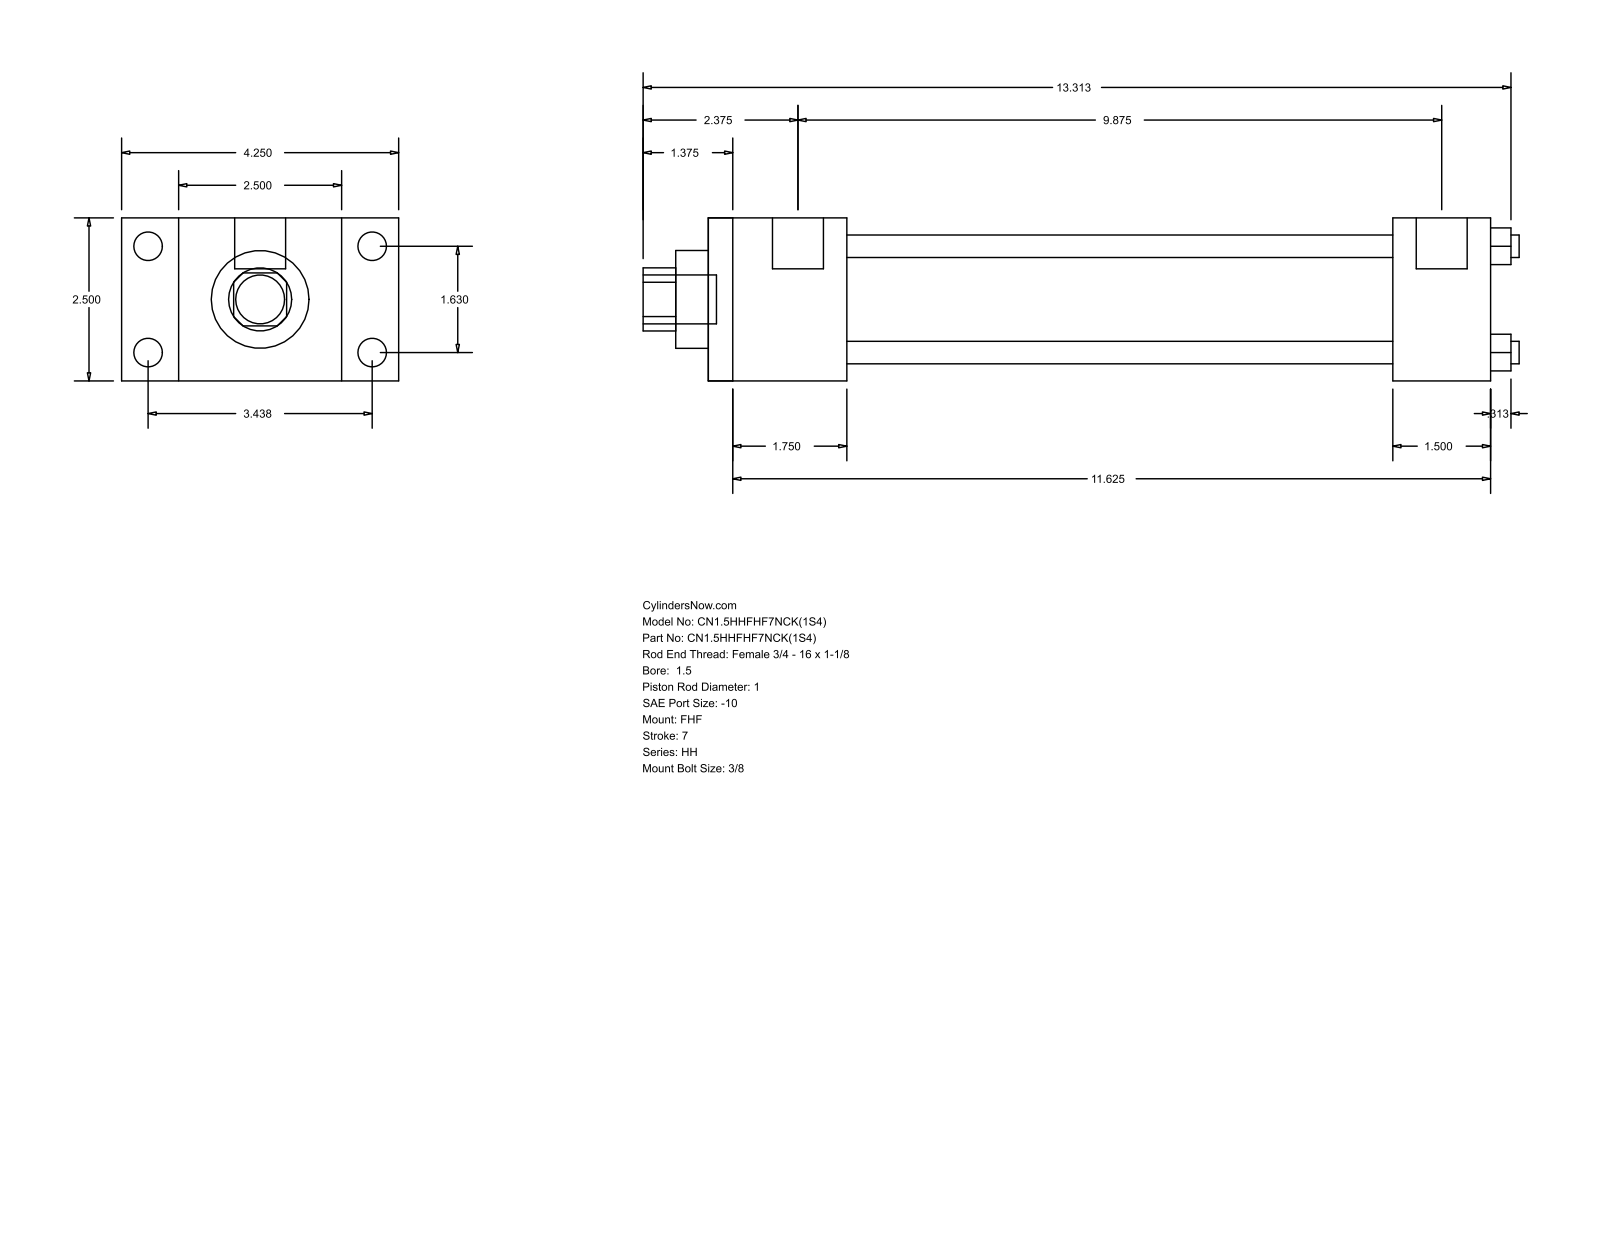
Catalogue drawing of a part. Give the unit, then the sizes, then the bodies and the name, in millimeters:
Units: millimetres
Overall size (bounding box): 341.31 × 107.95 × 63.5
Round holes (diameter × count): ⌀8.76 ×4, ⌀25.4 ×1, ⌀38.1 ×1, ⌀44.45 ×1
Round bosses / shafts (diameter × count): ⌀11.13 ×4, ⌀5.56 ×4, ⌀19.84 ×2, ⌀19.05 ×1
Partial cylindrical surfaces — rounded edges, fillets, slot ends (radius × count): R12.29 ×1
Main face-to-face distances: 63.5, 22.23, 85.73, 53.98, 107.96, 304.8, 250.82, 266.7, 212.72, 38.1
Hole centre spacings: 29.27, 41.4, 58.55
Bodies: 0 solids, 88 faces (60 planar, 28 cylindrical, 0 other)
Part name (STEP PRODUCT): HH_FHF__0150_1
STEP written by: GSSL Pune (CONFIG_CONTROL_DESIGN)
